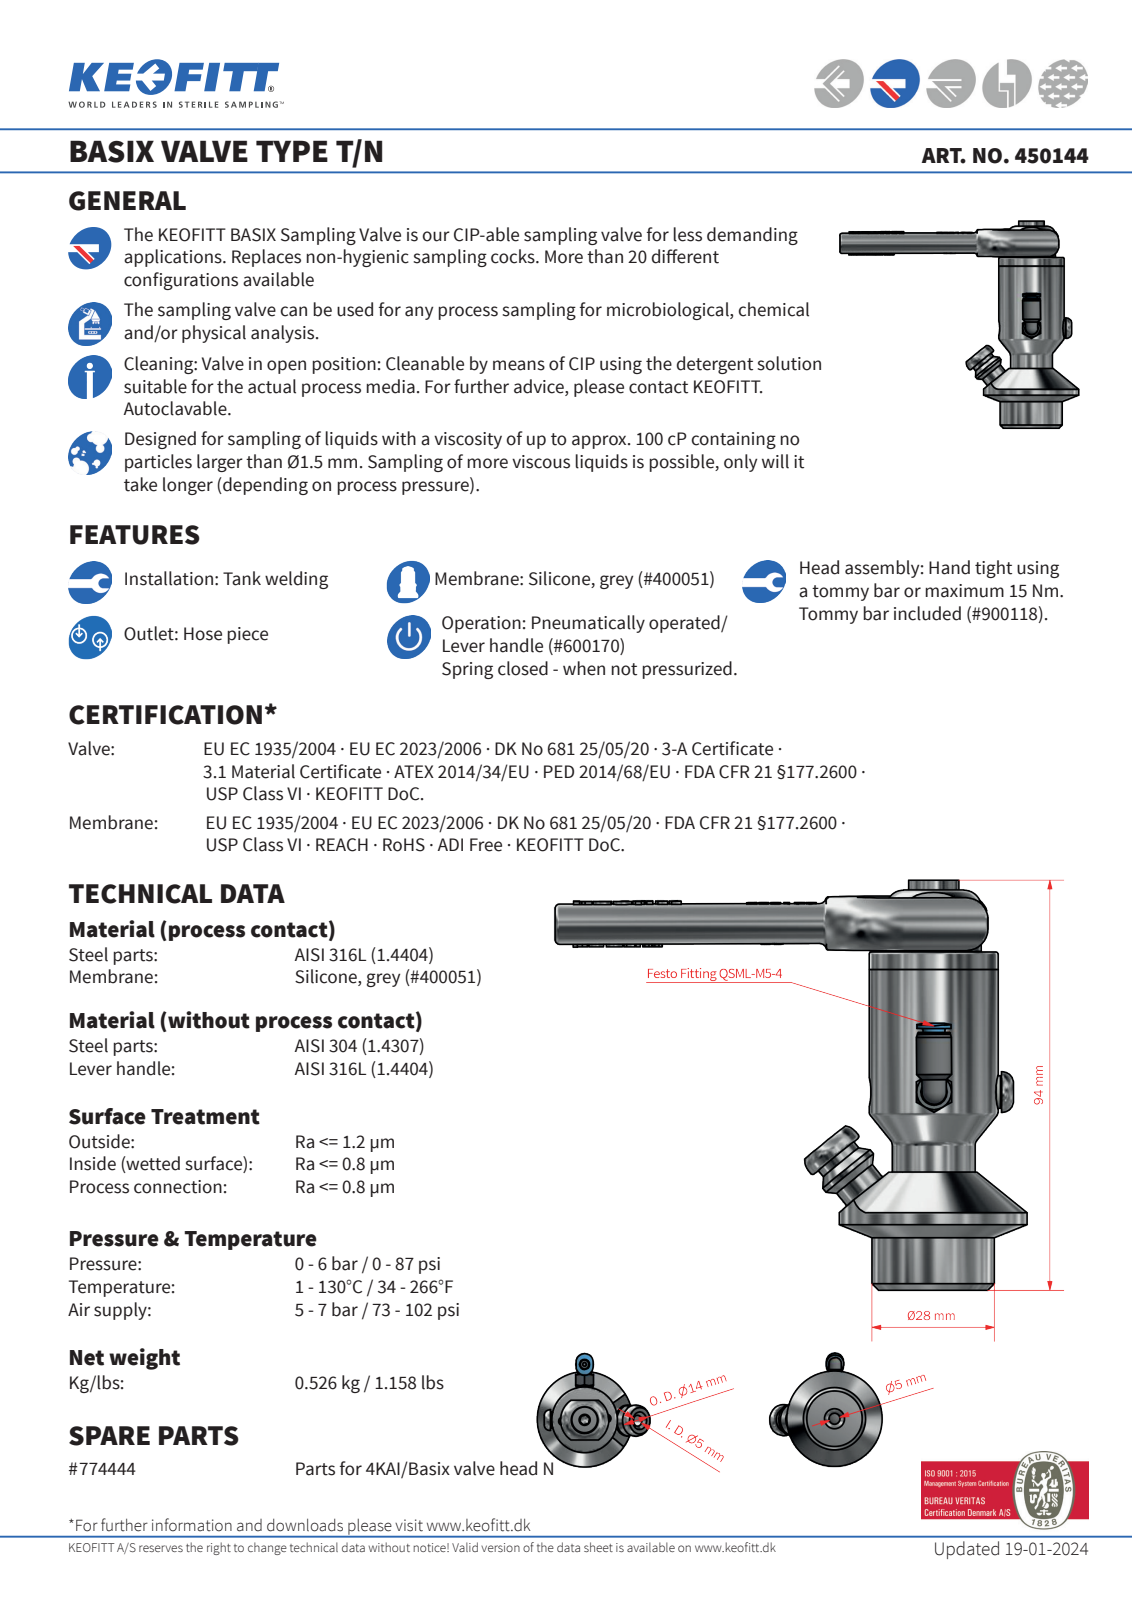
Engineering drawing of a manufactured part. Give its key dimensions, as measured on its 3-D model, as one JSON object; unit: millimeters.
{"part_name": "450144", "step_written_by": "Autodesk Inventor 2020 (AUTOMOTIVE_DESIGN)", "units": "millimeters", "bodies": {"solids": 1, "faces": 678, "planar": 278, "cylindrical": 108, "other": 292}, "overall_size": [116.28, 91.17, 51.73], "volume_mm3": 68671, "surface_area_mm2": 21622, "round_holes": [[1.7, 2], [4.3, 2], [5, 2], [8, 2], [4, 1], [5.05, 1], [6.05, 1], [10.1, 1], [12, 1], [20, 1], [22.5, 1], [24.5, 1]], "round_bosses_or_shafts": [[6, 3], [5, 3], [29.5, 2], [14, 2], [10.5, 2], [7.4, 2], [5.6, 2], [43, 1]], "partial_cylinders_radius": [[0.5, 14], [0.52, 7], [1.5, 4], [3, 4], [1, 2], [3.9, 2], [5, 2], [8, 2]], "face_to_face_distances": [9, 77.17, 12, 1.54, 10.54, 10.46, 1.46, 4, 3.1, 0.7]}
